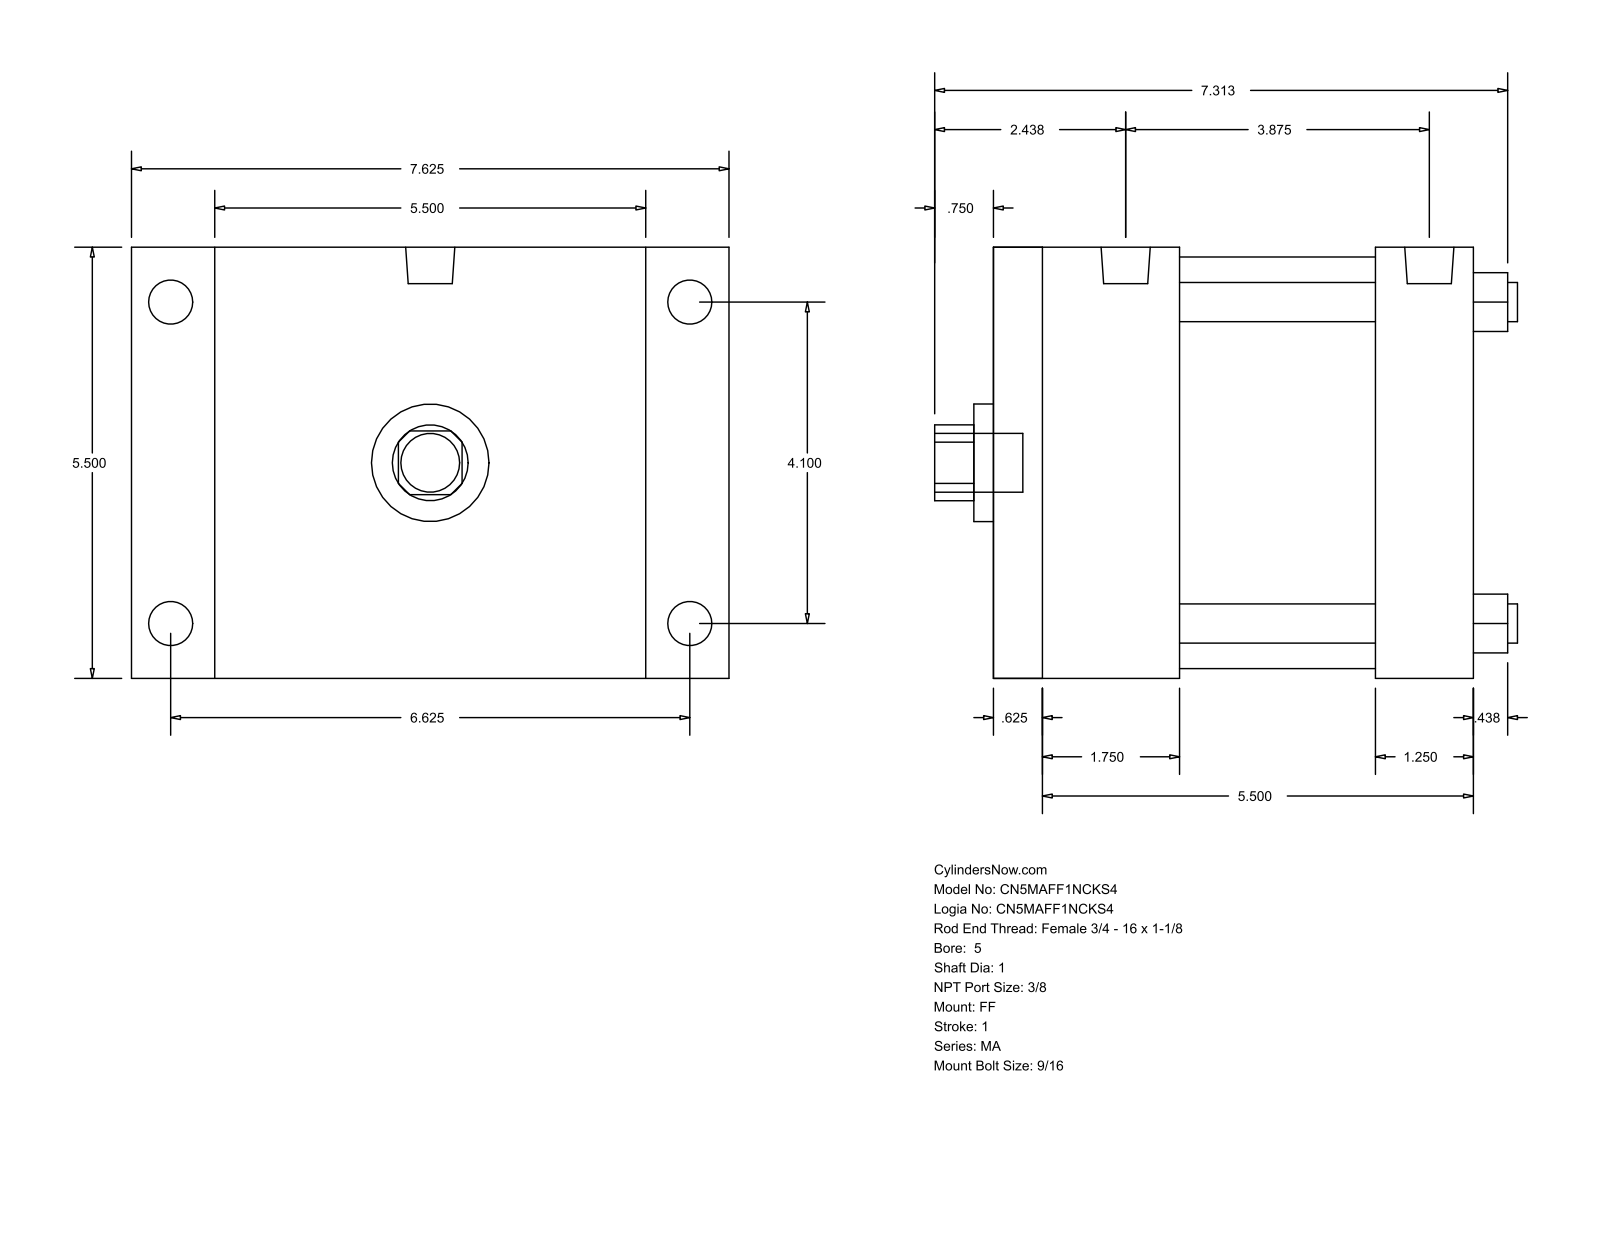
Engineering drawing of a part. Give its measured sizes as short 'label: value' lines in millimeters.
name: MA_FF__0500_1
written by: GSSL Pune (CONFIG_CONTROL_DESIGN)
unit: mm
bodies: 0 solids, 92 faces (64 planar, 28 cylindrical, 0 other)
size: 193.68 × 188.91 × 139.7
holes: 4× ⌀12.7, 1× ⌀25.4, 1× ⌀38.1, 1× ⌀133.35
bosses: 4× ⌀14.29, 4× ⌀11.11, 2× ⌀15.93, 1× ⌀19.05
rounds: 1× R12.29
face distances: 139.7, 155.57, 15.87, 166.69, 123.83, 107.96, 31.74, 60.33, 44.46, 63.5
hole spacings: 73.64, 104.14, 147.28
